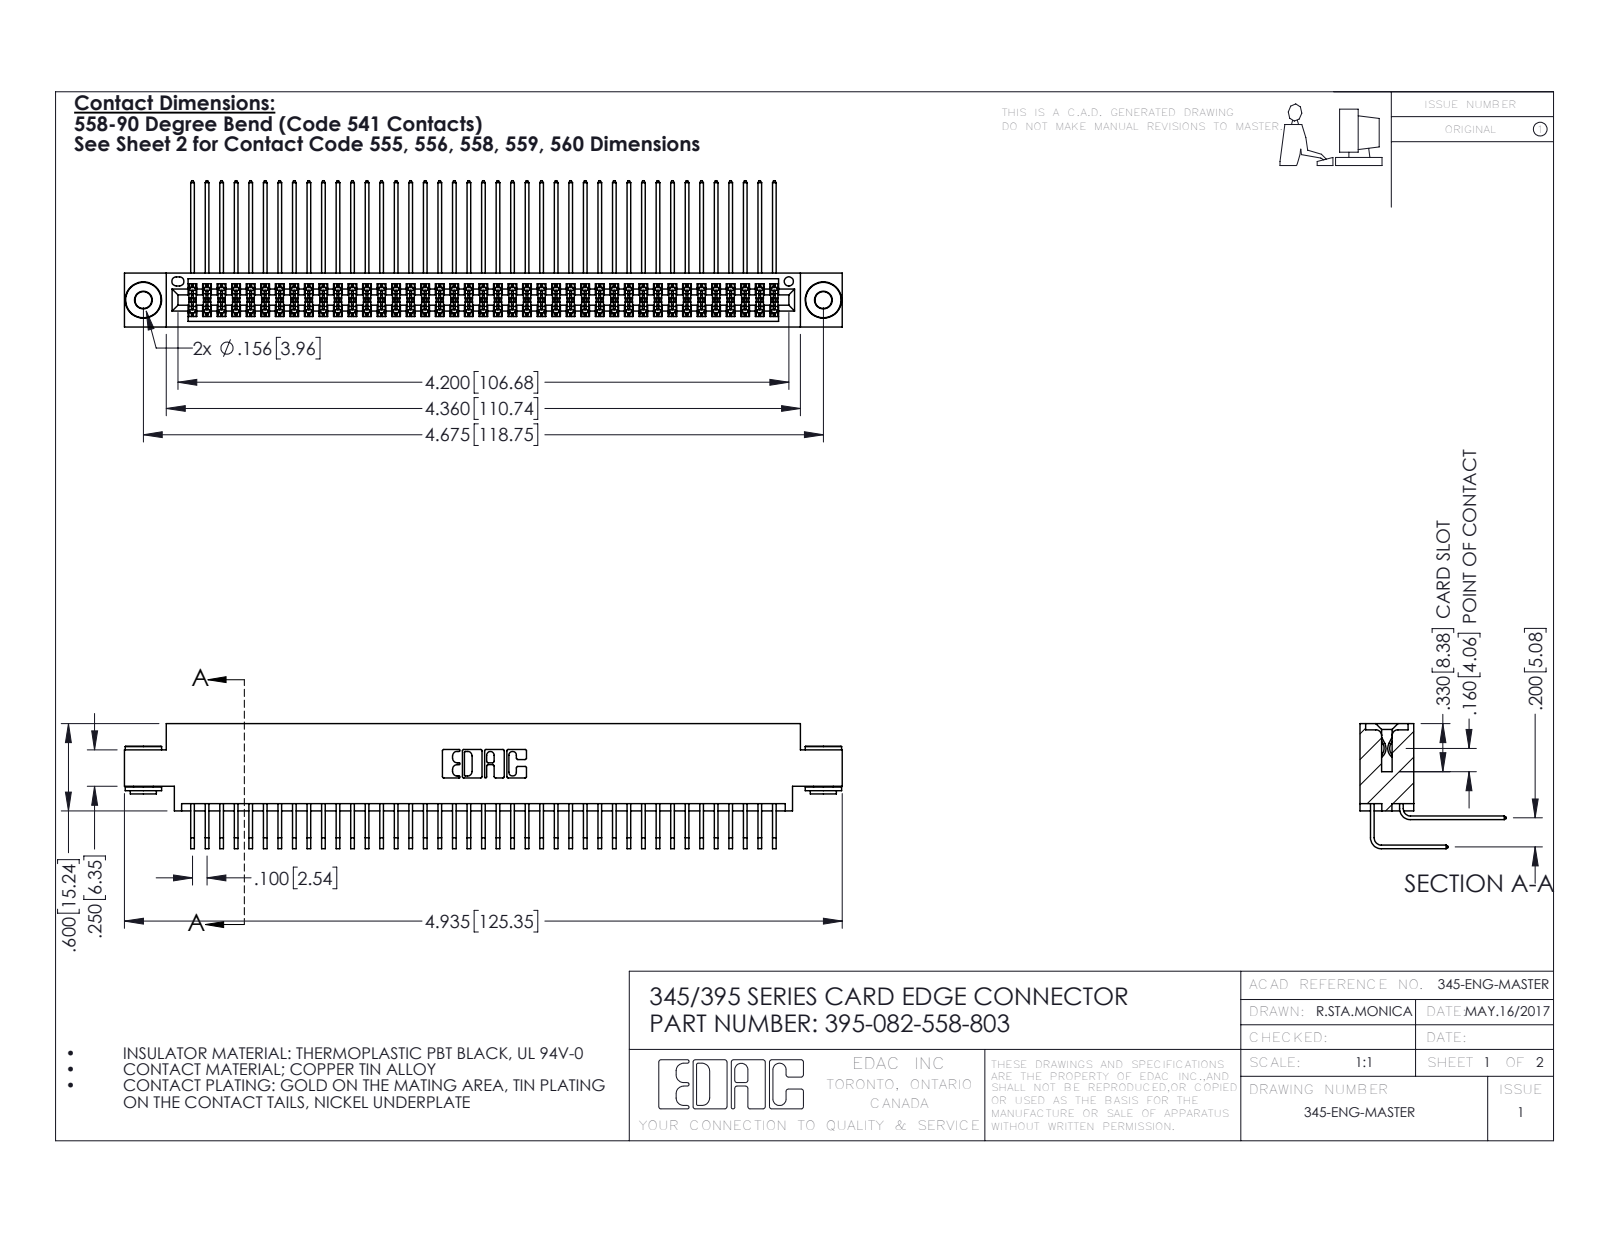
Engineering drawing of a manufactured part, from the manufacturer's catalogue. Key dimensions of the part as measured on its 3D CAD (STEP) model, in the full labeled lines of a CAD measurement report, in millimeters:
Part name (STEP PRODUCT): 345-292-001_558 Tail - 2; 395-082-558-803; 345-250-002_345-250-002-102; 345-292-001_558 559 Tail - 1 (+1 more)
STEP written by: SolidWorks 2016 (CONFIG_CONTROL_DESIGN)
Units: millimetres
Bodies: 85 solids, 4432 faces (2964 planar, 1460 cylindrical, 8 other)
Overall size (bounding box): 125.3 × 25.5 × 21.8
Volume: 12 600 mm³ · Surface area: 21 100 mm²
Round holes (diameter × count): ⌀2.9 ×2, ⌀4 ×2, ⌀1.6 ×1
Round bosses / shafts (diameter × count): ⌀6.4 ×2, ⌀4.6 ×2, ⌀3.5 ×2
Partial cylindrical surfaces — rounded edges, fillets, slot ends (radius × count): R0.2 ×124, R0.3 ×22, R0.2 ×6, R0.8 ×6, R0.7 ×3, R0.4 ×2, R0.5 ×2, R0.6 ×2
Main face-to-face distances: 1.8, 7.6, 5.1, 9.4, 2.5, 6.9, 0.6, 5.7, 4.4, 0.6
Hole centre spacings: 6.9, 112.8, 118.7
